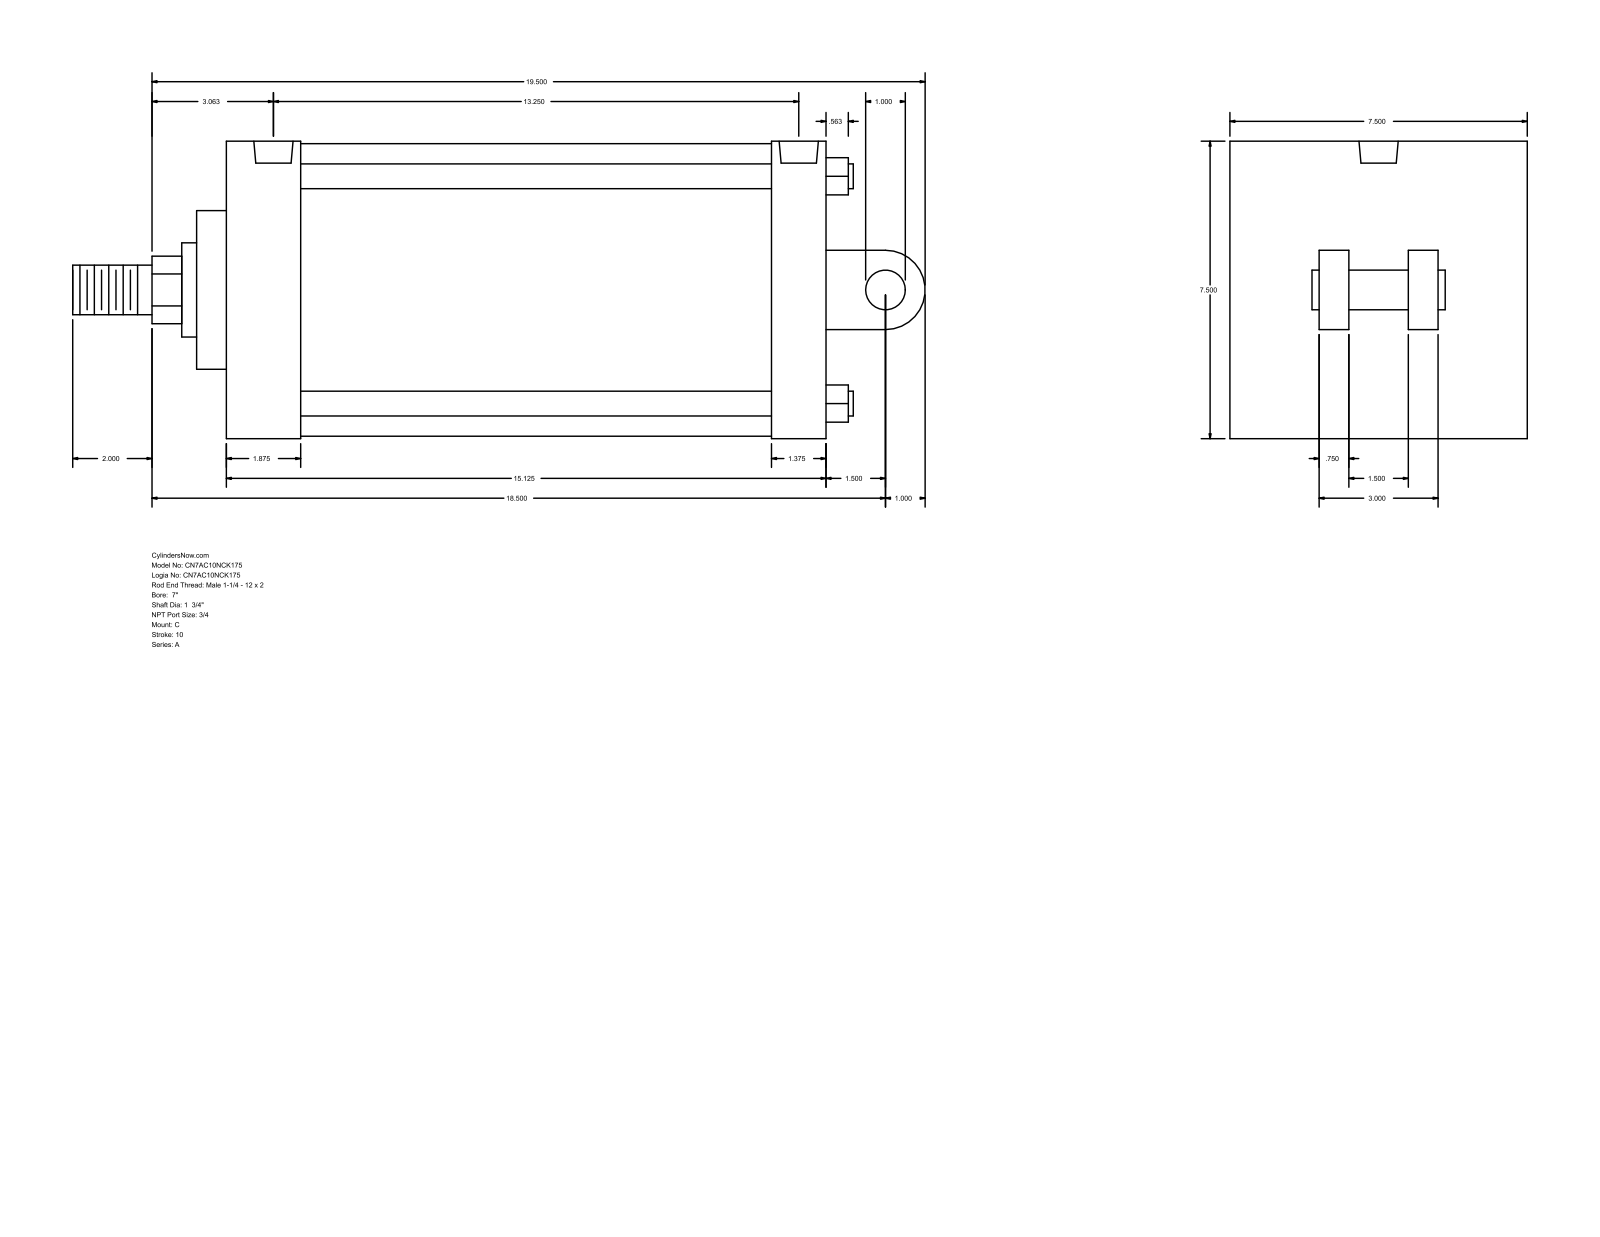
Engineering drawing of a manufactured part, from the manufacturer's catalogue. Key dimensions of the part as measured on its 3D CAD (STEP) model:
Part name (STEP PRODUCT): A_C__0700_1.75
STEP written by: GSSL Pune (CONFIG_CONTROL_DESIGN)
Units: millimetres
Bodies: 0 solids, 104 faces (75 planar, 29 cylindrical, 0 other)
Overall size (bounding box): 546.1 × 190.5 × 190.5
Round holes (diameter × count): ⌀15.08 ×4, ⌀25.12 ×2
Round bosses / shafts (diameter × count): ⌀15.88 ×4, ⌀187.32 ×1, ⌀60.33 ×1, ⌀44.45 ×1, ⌀31.75 ×1, ⌀25.4 ×1
Partial cylindrical surfaces — rounded edges, fillets, slot ends (radius × count): R21.63 ×1, R25.4 ×1
Main face-to-face distances: 190.5, 384.18, 19.05, 76.2, 57.15, 146.05, 44.45, 69.85, 47.63, 336.55
Hole centre spacings: 5.56, 325.43, 330.99, 336.55
